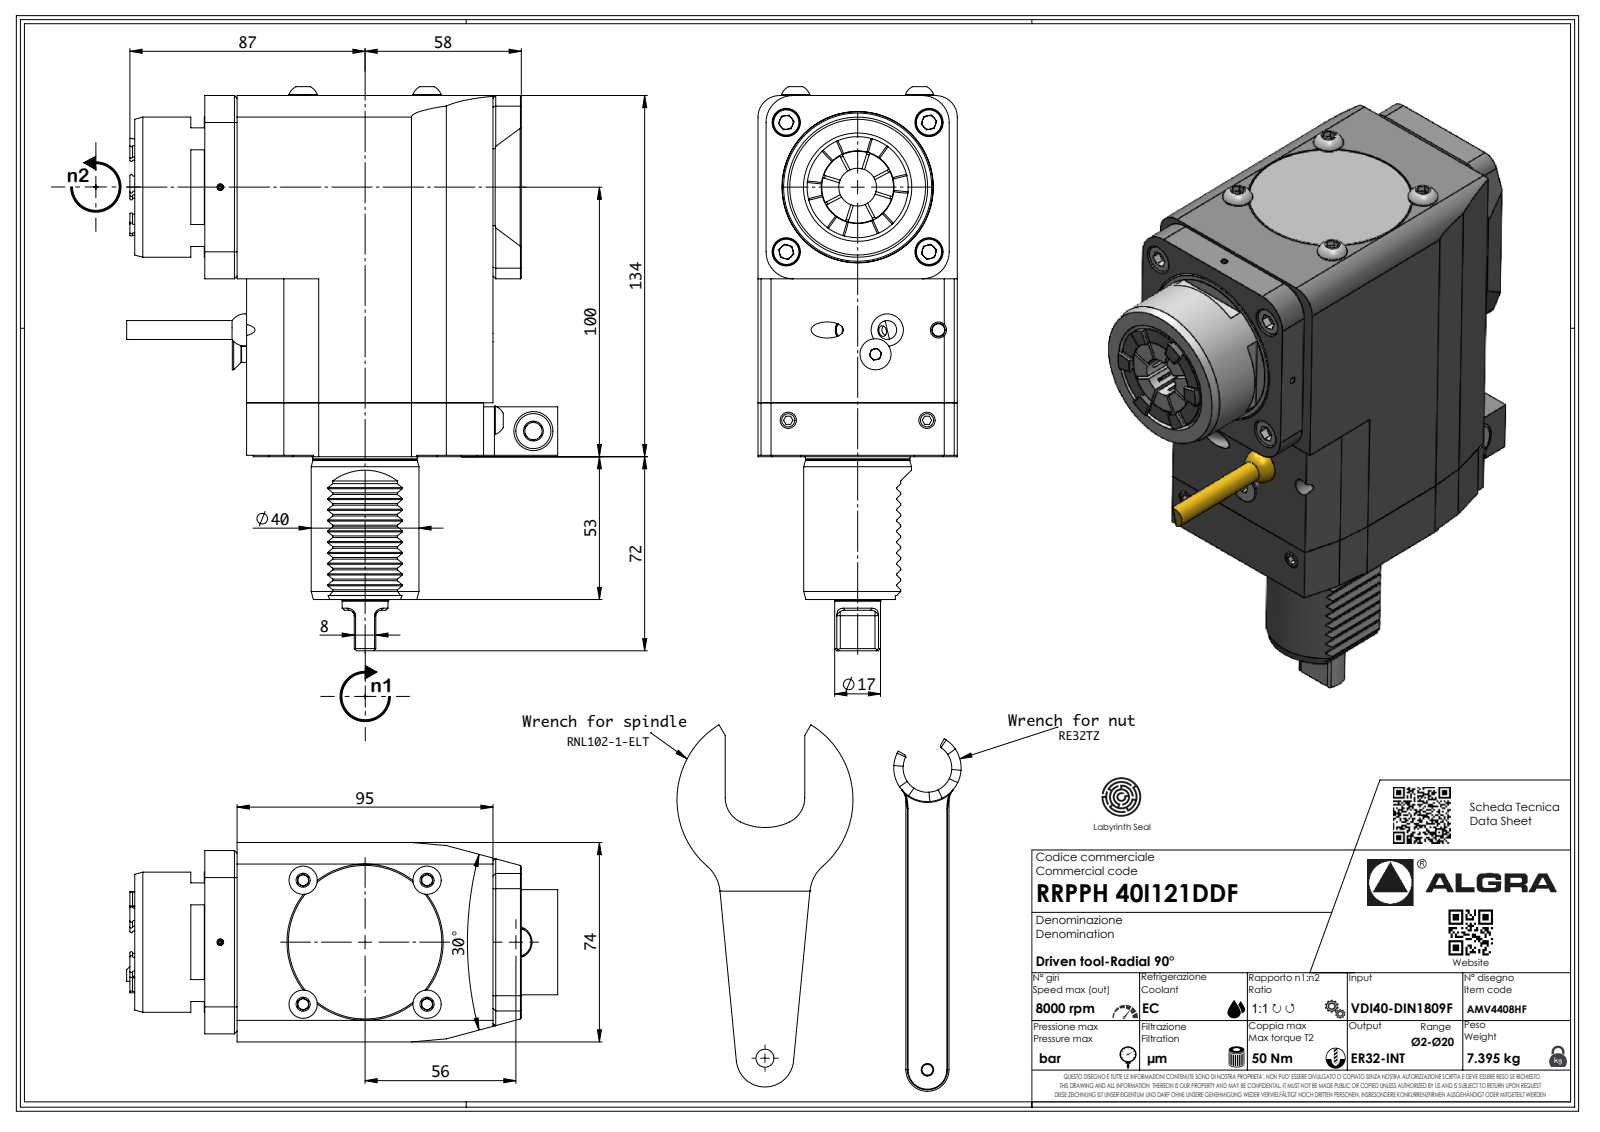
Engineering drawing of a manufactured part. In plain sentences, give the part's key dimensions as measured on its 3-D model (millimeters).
The part is named "RRPPH40I121DDF". Its 3-D file was written by "SolidWorks 2023 (AUTOMOTIVE_DESIGN)". It is 1 solid with 767 faces: 485 planar, 134 cylindrical and 148 other. Overall it measures 209.3 by 159.5 by 74 millimeters. Its volume is 1 122 000 cubic millimeters and its surface area 88 281 square millimeters. Round holes: 6 of diameter 5, 4 of diameter 4.2, 4 of diameter 5.5, 4 of diameter 6.2, 4 of diameter 7, 4 of diameter 9, 4 of diameter 10.5, 3 of diameter 6, 2 of diameter 2.5, 2 of diameter 4, 1 of diameter 1.2, 1 of diameter 2.1. Round bosses or shafts: 6 of diameter 10.5, 2 of diameter 6, 1 of diameter 52, 1 of diameter 40, 1 of diameter 38.7, 1 of diameter 30, 1 of diameter 28.34, 1 of diameter 17. Partial cylindrical surfaces (rounded edges, fillets, slot ends): 11 of radius 0.3, 7 of radius 0.33, 7 of radius 0.52, 7 of radius 3.7, 6 of radius 2, 4 of radius 6, 4 of radius 10, 2 of radius 8. The main face-to-face distances are 74, 134, 91.5, 102, 10.5, 41.5, 117.5, 15.5, 107, 68. The hole center spacings are 7.55, 34.83, 35.75, 47, 52.67, 70.18, 8, 21.71.
